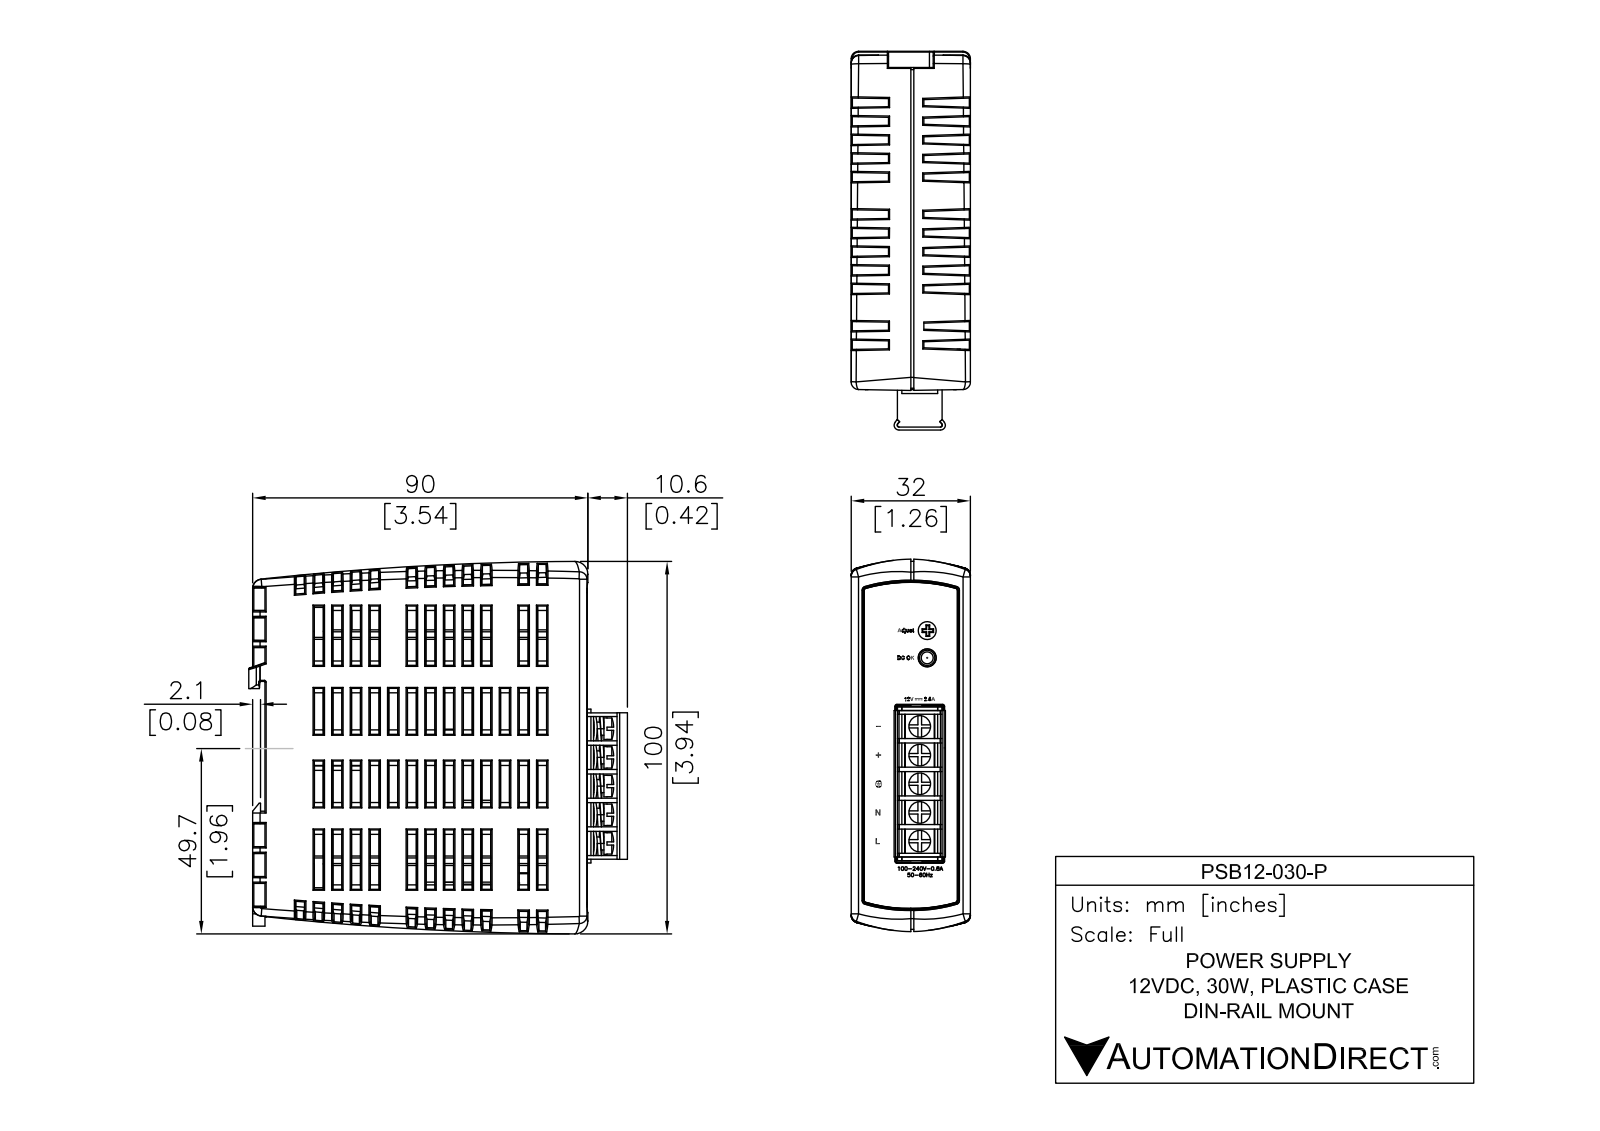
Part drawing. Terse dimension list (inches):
name: PSB12-030-P
written by: SolidWorks 2011 (CONFIG_CONTROL_DESIGN)
unit: in
bodies: 1 solid, 1228 faces (965 planar, 55 cylindrical, 208 other)
size: 3.97 × 3.943 × 1.26
volume: 11.69 in³; area: 93.59 in²
holes: 2× ⌀0.175
bosses: 5× ⌀0.202, 1× ⌀0.094
rounds: 10× R0.015, 6× R0.06, 2× R0.03, 2× R0.033, 1× R1.75
face distances: 0.89, 0.37, 1.26, 0.08, 1.18, 0.29, 0.4, 0.799, 1.199, 0.2
hole spacings: 0.3
